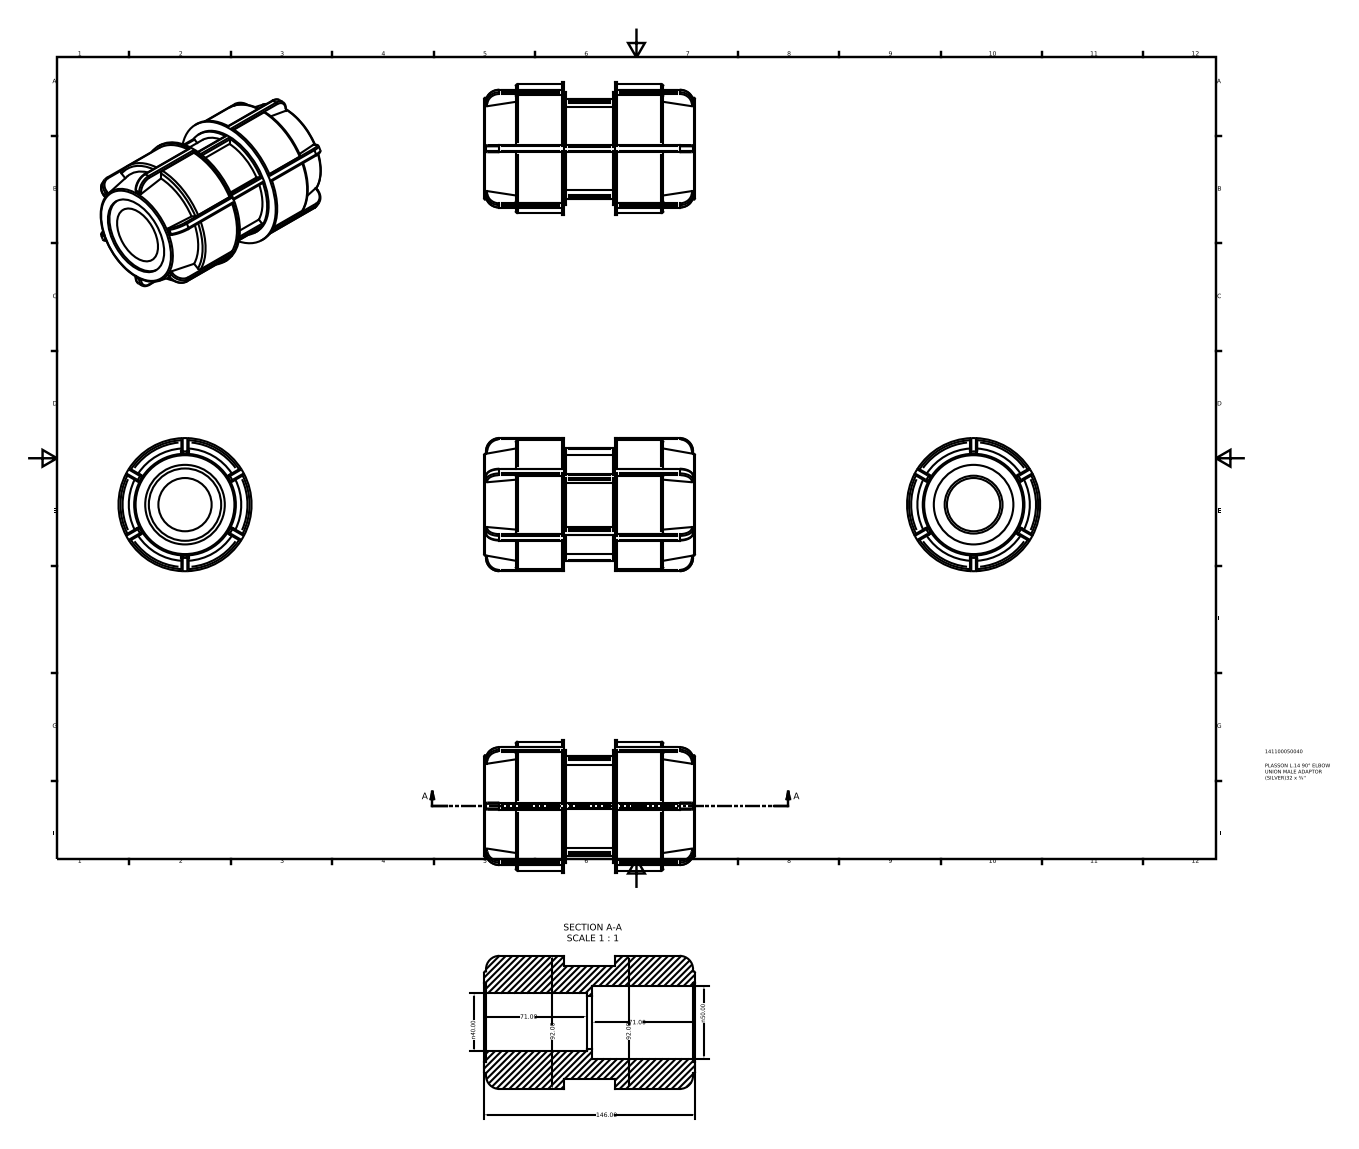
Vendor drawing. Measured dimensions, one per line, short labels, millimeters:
name: 141100050040
written by: Autodesk Inventor 2015 (AUTOMOTIVE_DESIGN)
unit: mm
bodies: 1 solid, 230 faces (92 planar, 86 cylindrical, 52 other)
size: 146 × 92 × 92
volume: 524 102 mm³; area: 78 112 mm²
holes: 1× ⌀36.8, 1× ⌀40, 1× ⌀50, 1× ⌀55
bosses: 1× ⌀92, 1× ⌀89.24, 1× ⌀78.2, 1× ⌀69
rounds: 36× R0.92
face distances: 35.04, 1.46, 55.48, 33.58, 89.06, 90.52, 54.02, 21.9, 124.1, 68.62
